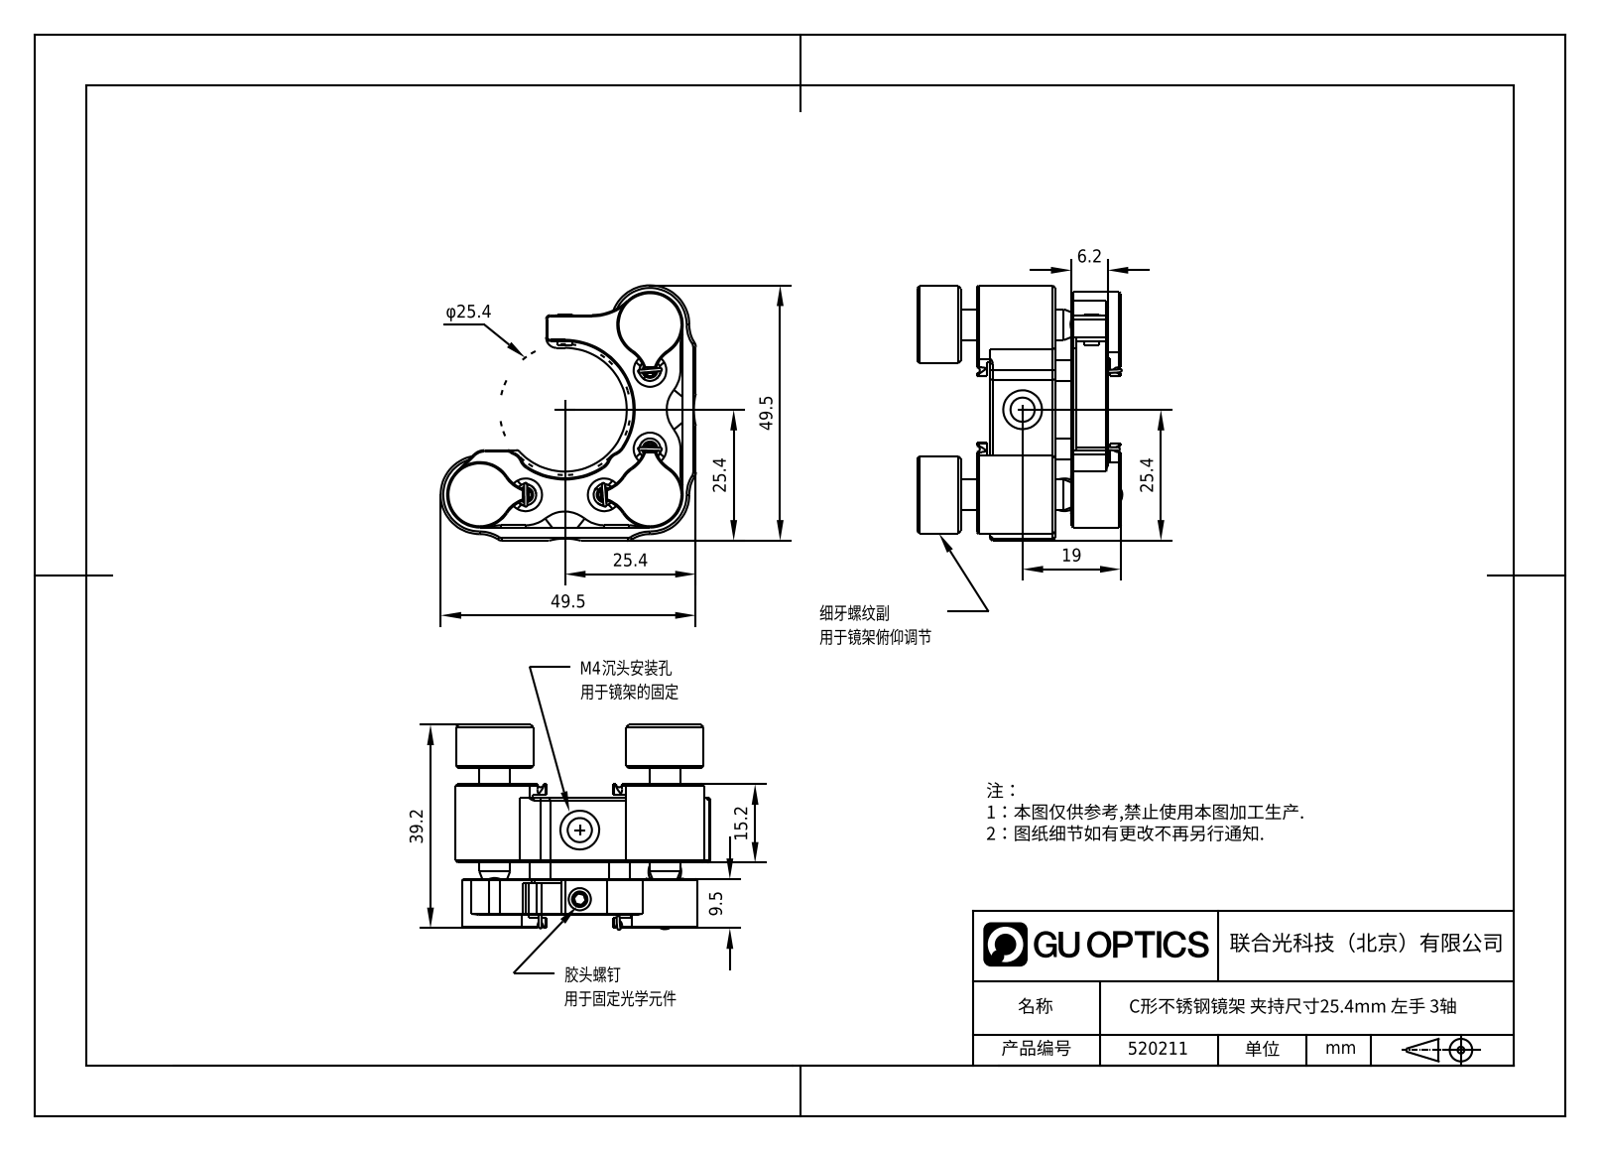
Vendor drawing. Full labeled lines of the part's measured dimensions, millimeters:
Part name (STEP PRODUCT): 520211
STEP written by: SolidWorks 2020 (CONFIG_CONTROL_DESIGN)
Units: millimetres
Bodies: 30 solids, 566 faces (237 planar, 119 cylindrical, 210 other)
Overall size (bounding box): 49.53 × 49.53 × 39.83
Volume: 24 607 mm³ · Surface area: 16 960 mm²
Round holes (diameter × count): ⌀6.35 ×7, ⌀2.4 ×4, ⌀3.99 ×3, ⌀4 ×3, ⌀6 ×3, ⌀7 ×3, ⌀2.01 ×2, ⌀4.7 ×2, ⌀7.54 ×2, ⌀3.3 ×1
Round bosses / shafts (diameter × count): ⌀4 ×11, ⌀15 ×3, ⌀15.24 ×2, ⌀12.7 ×2, ⌀3 ×1
Partial cylindrical surfaces — rounded edges, fillets, slot ends (radius × count): R6.48 ×22, R3 ×5, R0.8 ×4, R1 ×4, R1.93 ×4, R3.17 ×4, R1.59 ×2, R1.59 ×2
Main face-to-face distances: 2.54, 25.22, 3, 21.5, 6.98, 18.24, 12.7, 15.24, 9.98, 14.3
Hole centre spacings: 8.89, 24.13, 5, 15.24, 25.72, 33.02, 34.2, 40.9
